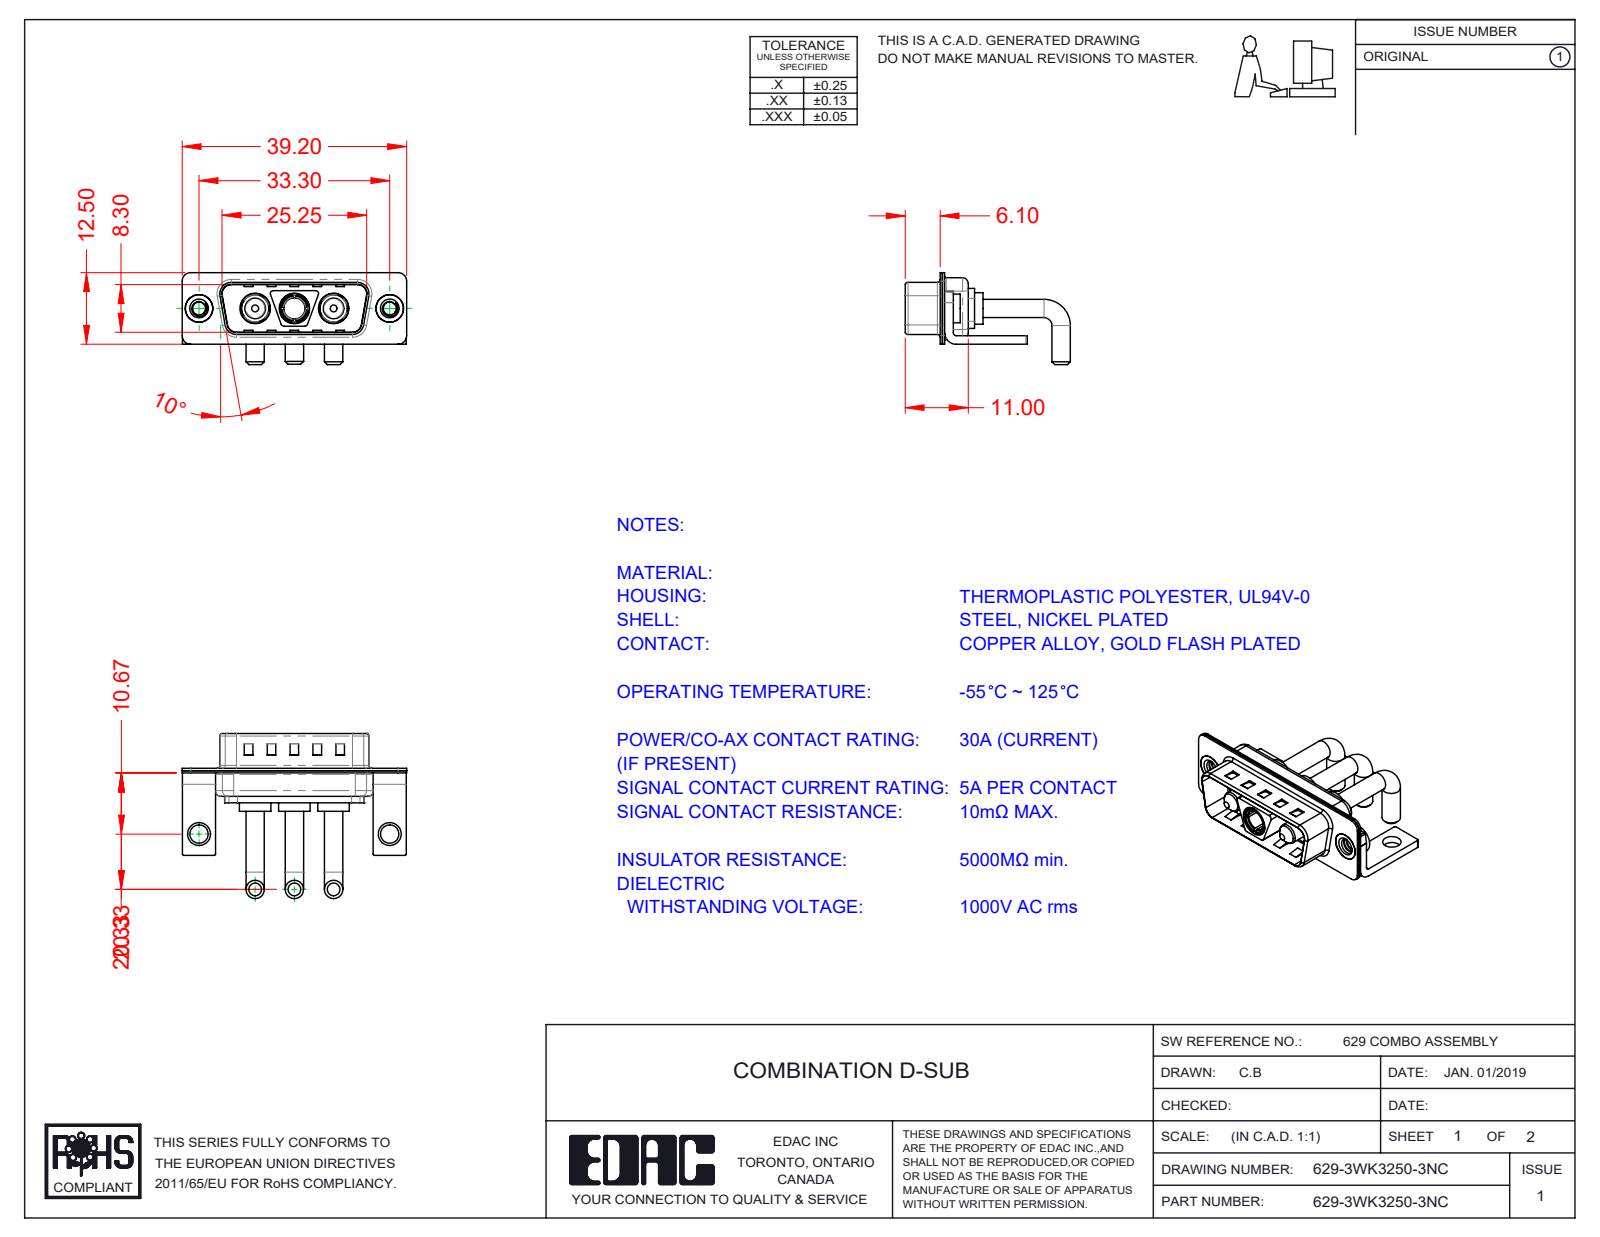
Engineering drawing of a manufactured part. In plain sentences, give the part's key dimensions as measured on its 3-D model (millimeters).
The part is named "Power Pin_Ext 30A RA; Power Socket_Ext 30A RA; 629Combo Shell Front_15 Contacts; 629Combo Shell Rear_15 Contacts (+4 more)". Its 3-D file was written by "SolidWorks 2020 (CONFIG_CONTROL_DESIGN)". It is 13 solids with 562 faces: 213 planar, 229 cylindrical and 120 other. Overall it measures 39.2 by 28.83 by 16.05 millimeters. Its volume is 2 922 cubic millimeters and its surface area 6 275 square millimeters. Round holes: 3 of diameter 4.85, 3 of diameter 5.3, 2 of diameter 2.26, 2 of diameter 3.2, 2 of diameter 4, 2 of diameter 4.8, 1 of diameter 3.7. Round bosses or shafts: 6 of diameter 3.2, 3 of diameter 5.5, 3 of diameter 5.2, 3 of diameter 4.75, 3 of diameter 3.75, 2 of diameter 5, 2 of diameter 4.9, 2 of diameter 3.6. Partial cylindrical surfaces (rounded edges, fillets, slot ends): 16 of radius 0.25, 16 of radius 1.5, 13 of radius 0.5, 13 of radius 2, 8 of radius 1.6, 4 of radius 0.6, 4 of radius 0.65, 4 of radius 0.9. The main face-to-face distances are 0.4, 0.8, 1.5, 9.5, 9.1, 8.7, 9.9, 5.2, 1.2, 0.75. The hole center spacings are 6.85, 9.8, 16.65, 23.5, 33.3, 13.7.
